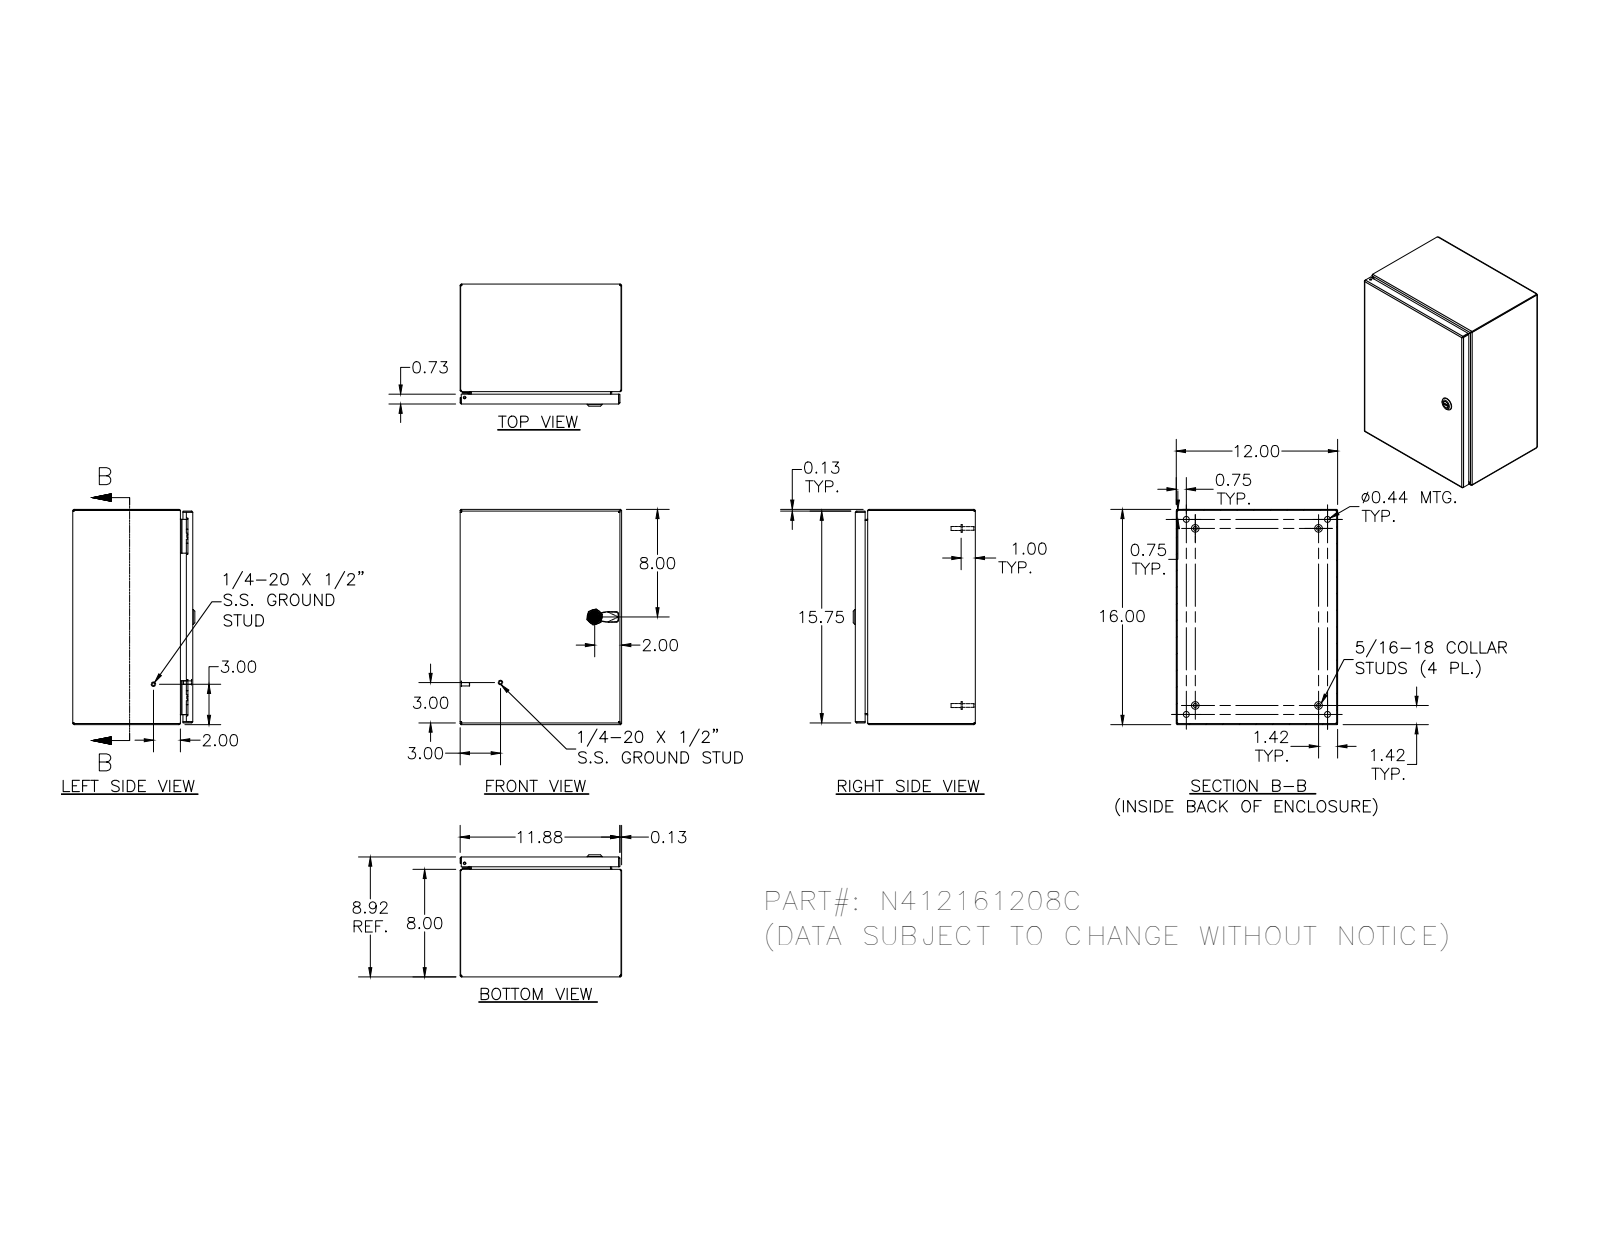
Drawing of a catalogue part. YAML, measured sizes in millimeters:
part_name: "N412161208C"
step_written_by: "SolidWorks 2018 (AUTOMOTIVE_DESIGN)"
units: millimeters
bodies: {solids: 33, faces: 1449, planar: 530, cylindrical: 547, other: 372}
overall_size: [406.4, 304.8, 230.5]
volume: 1155000
surface_area: 1239000
round_holes:
  - {diameter: 4.8, count: 5}
  - {diameter: 2.4, count: 4}
  - {diameter: 3.9, count: 4}
  - {diameter: 4.2, count: 4}
  - {diameter: 4.4, count: 4}
  - {diameter: 11.1, count: 4}
  - {diameter: 4, count: 2}
  - {diameter: 4.7, count: 1}
  - {diameter: 5, count: 1}
  - {diameter: 8, count: 1}
  - {diameter: 10, count: 1}
  - {diameter: 10.2, count: 1}
round_bosses_or_shafts:
  - {diameter: 6.4, count: 10}
  - {diameter: 14.3, count: 4}
  - {diameter: 9.1, count: 4}
  - {diameter: 8.1, count: 4}
  - {diameter: 7.6, count: 4}
  - {diameter: 7, count: 4}
  - {diameter: 6.5, count: 4}
  - {diameter: 4.2, count: 4}
partial_cylinders:
  - {radius: 0.3, count: 30}
  - {radius: 0.8, count: 30}
  - {radius: 1.3, count: 26}
  - {radius: 2.7, count: 20}
  - {radius: 0.4, count: 18}
  - {radius: 3.2, count: 16}
  - {radius: 0.5, count: 13}
  - {radius: 0.8, count: 8}
face_to_face_distances: [1.9, 224.6, 1.9, 222.7, 226.5, 302.9, 304.8, 301, 302.9, 404.5]
hole_center_spacings: [304.8, 16.8, 16.7, 33.2, 49.9, 12.7, 25, 33.3]
